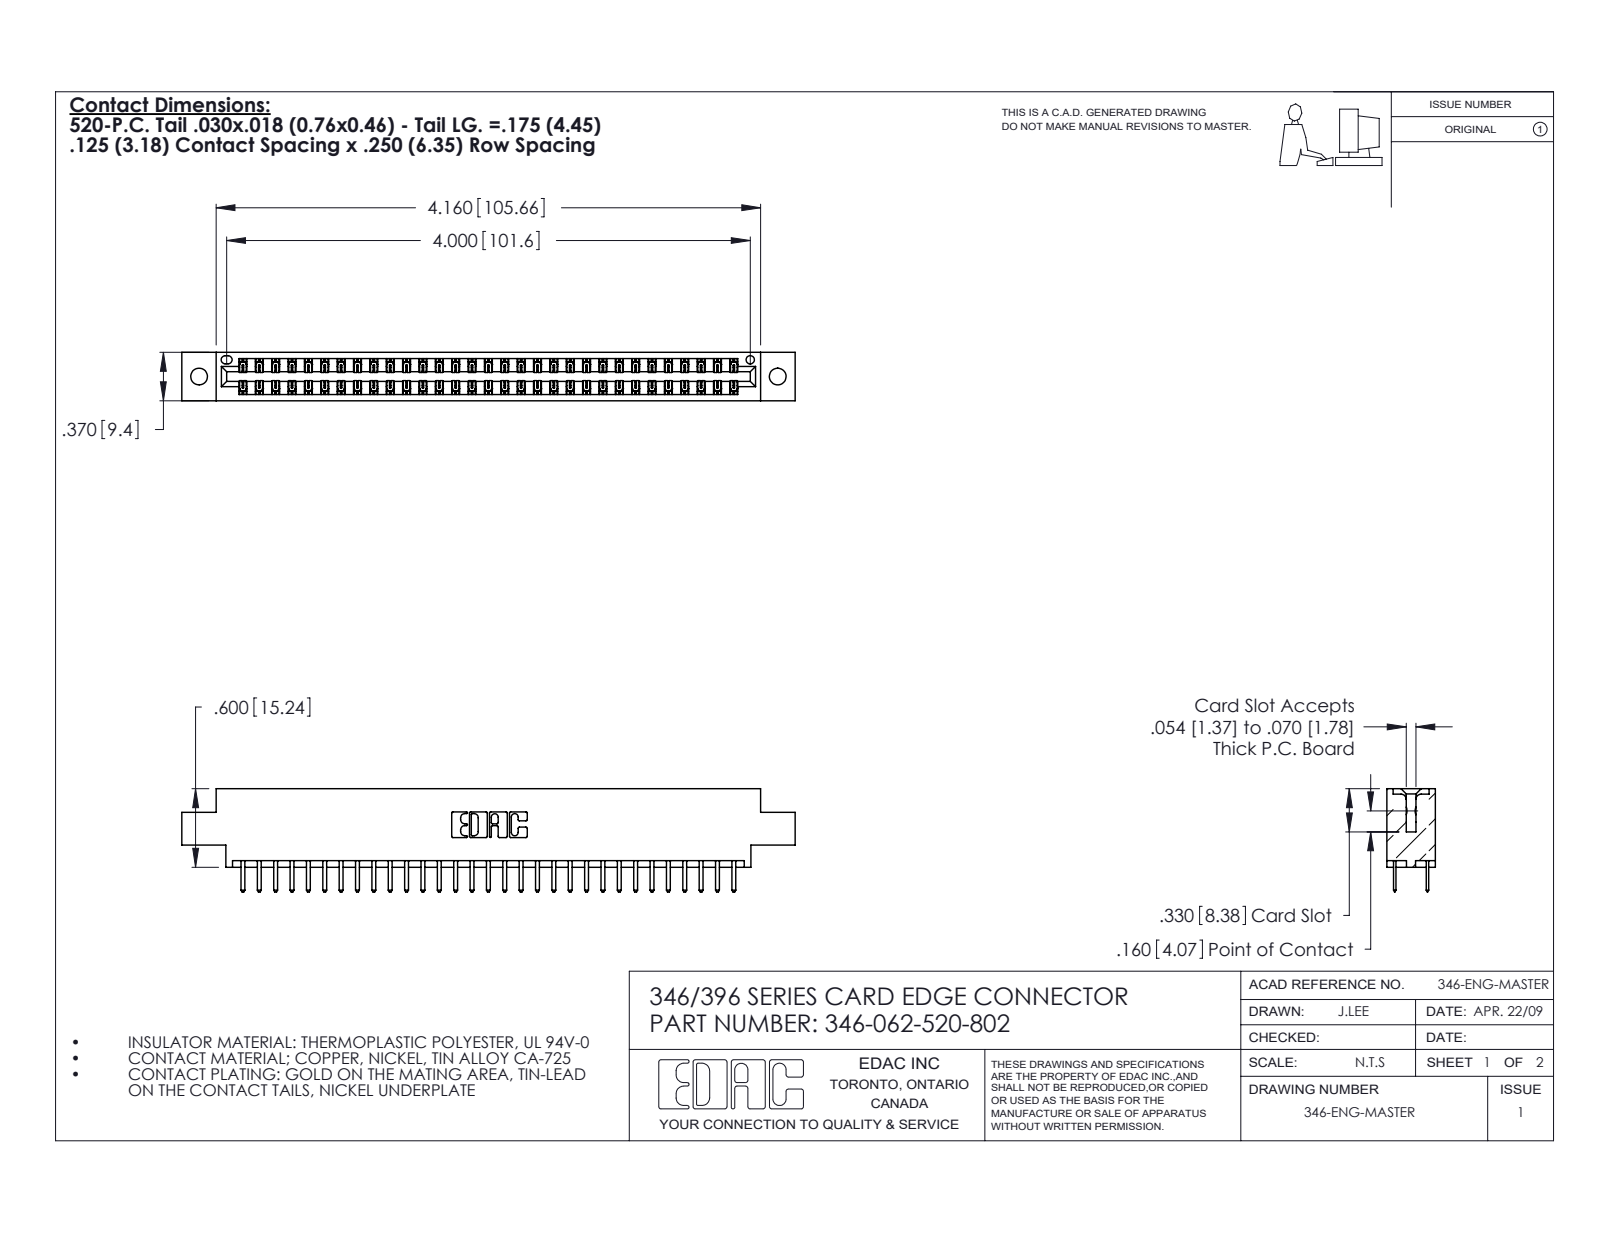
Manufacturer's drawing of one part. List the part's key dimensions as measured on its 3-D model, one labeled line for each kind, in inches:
Part name (STEP PRODUCT): 346-062-520-802; 345-292-001_345-293-120; 346 Part_0.170 Offset - 0.128 Dia
STEP written by: SolidWorks 2020 (CONFIG_CONTROL_DESIGN)
Units: inches
Bodies: 63 solids, 3598 faces (2374 planar, 1224 cylindrical, 0 other)
Overall size (bounding box): 4.685 × 0.788 × 0.37
Volume: 0.69 in³ · Surface area: 23.57 in²
Round holes (diameter × count): ⌀0.128 ×2, ⌀0.064 ×1
Partial cylindrical surfaces — rounded edges, fillets, slot ends (radius × count): R0.006 ×93, R0.01 ×66, R0.01 ×22, R0.007 ×6, R0.031 ×6, R0.026 ×3, R0.014 ×2, R0.022 ×2
Main face-to-face distances: 0.048, 0.322, 0.25, 0.37, 0.275, 0.072, 0.298, 0.025, 0.148, 0.222
Hole centre spacings: 0.246, 4.212, 4.42
